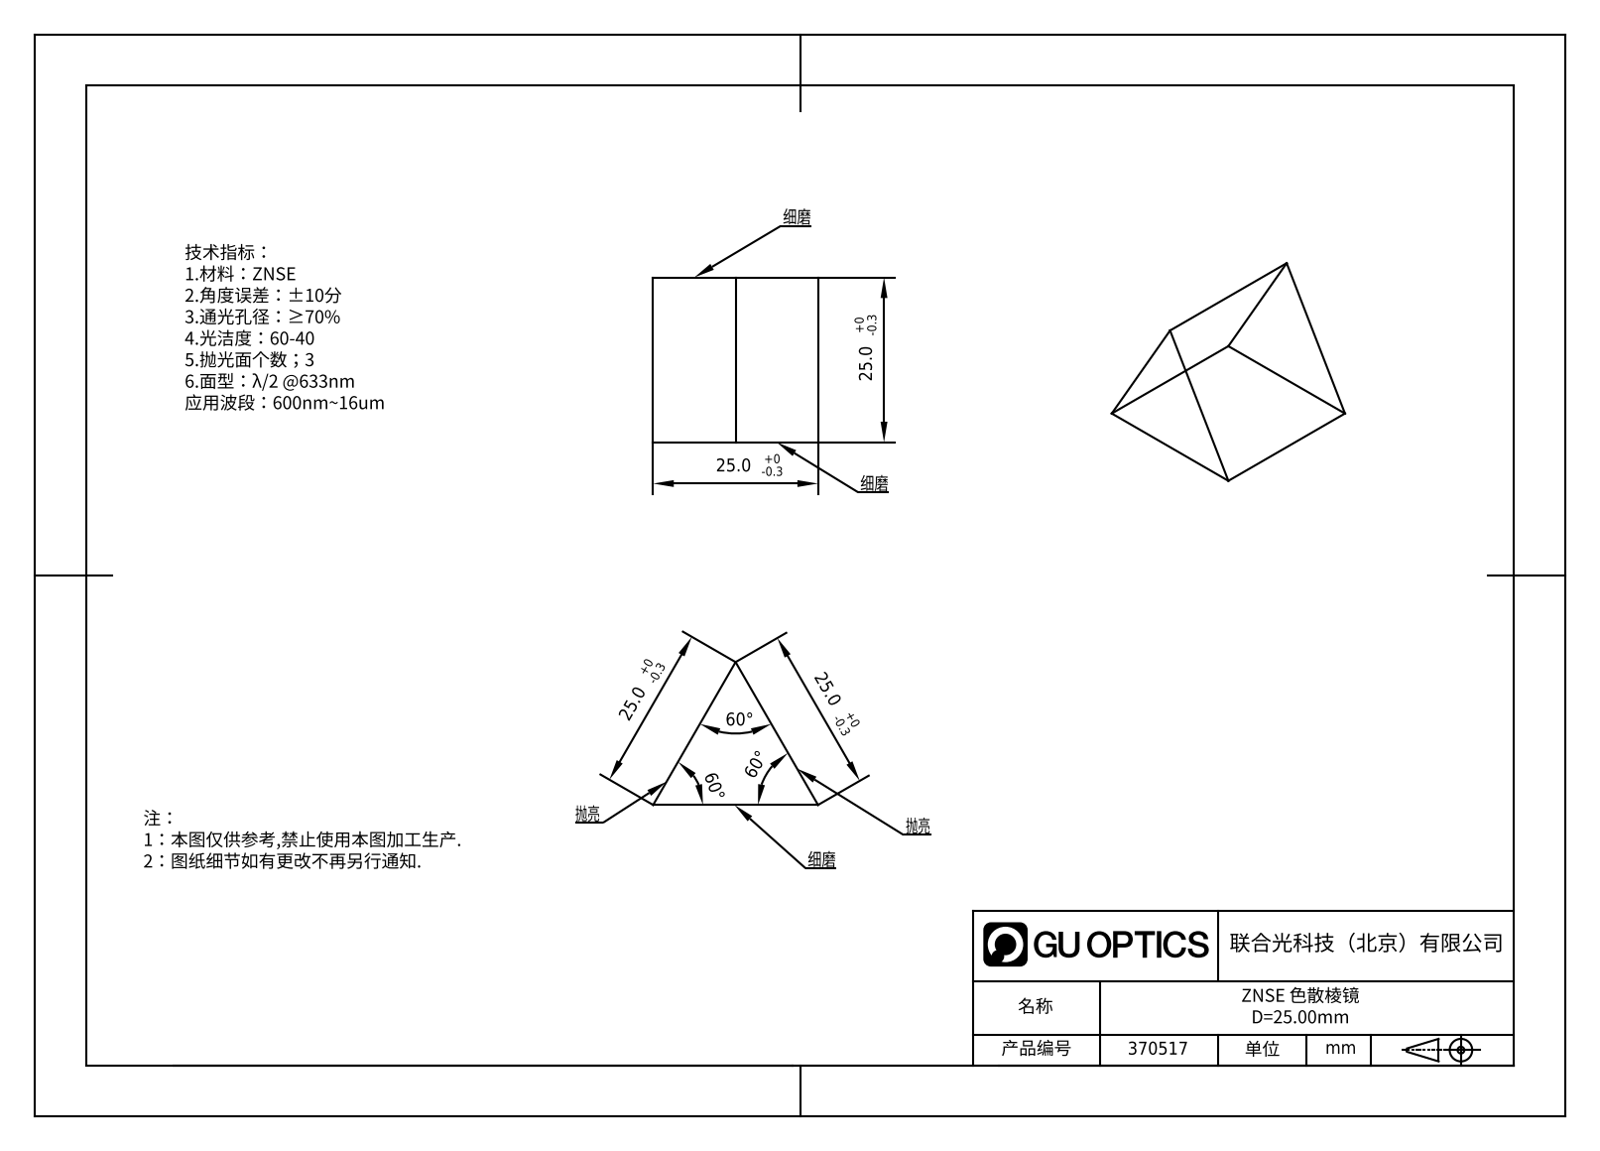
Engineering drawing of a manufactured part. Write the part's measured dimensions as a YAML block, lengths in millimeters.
part_name: "GPD-025-D"
step_written_by: "SolidWorks 2022 (AUTOMOTIVE_DESIGN)"
units: millimeters
bodies: {solids: 1, faces: 20, planar: 20, cylindrical: 0, other: 0}
overall_size: [25, 24.91, 21.59]
volume: 6765
surface_area: 2401
face_to_face_distances: [25]
